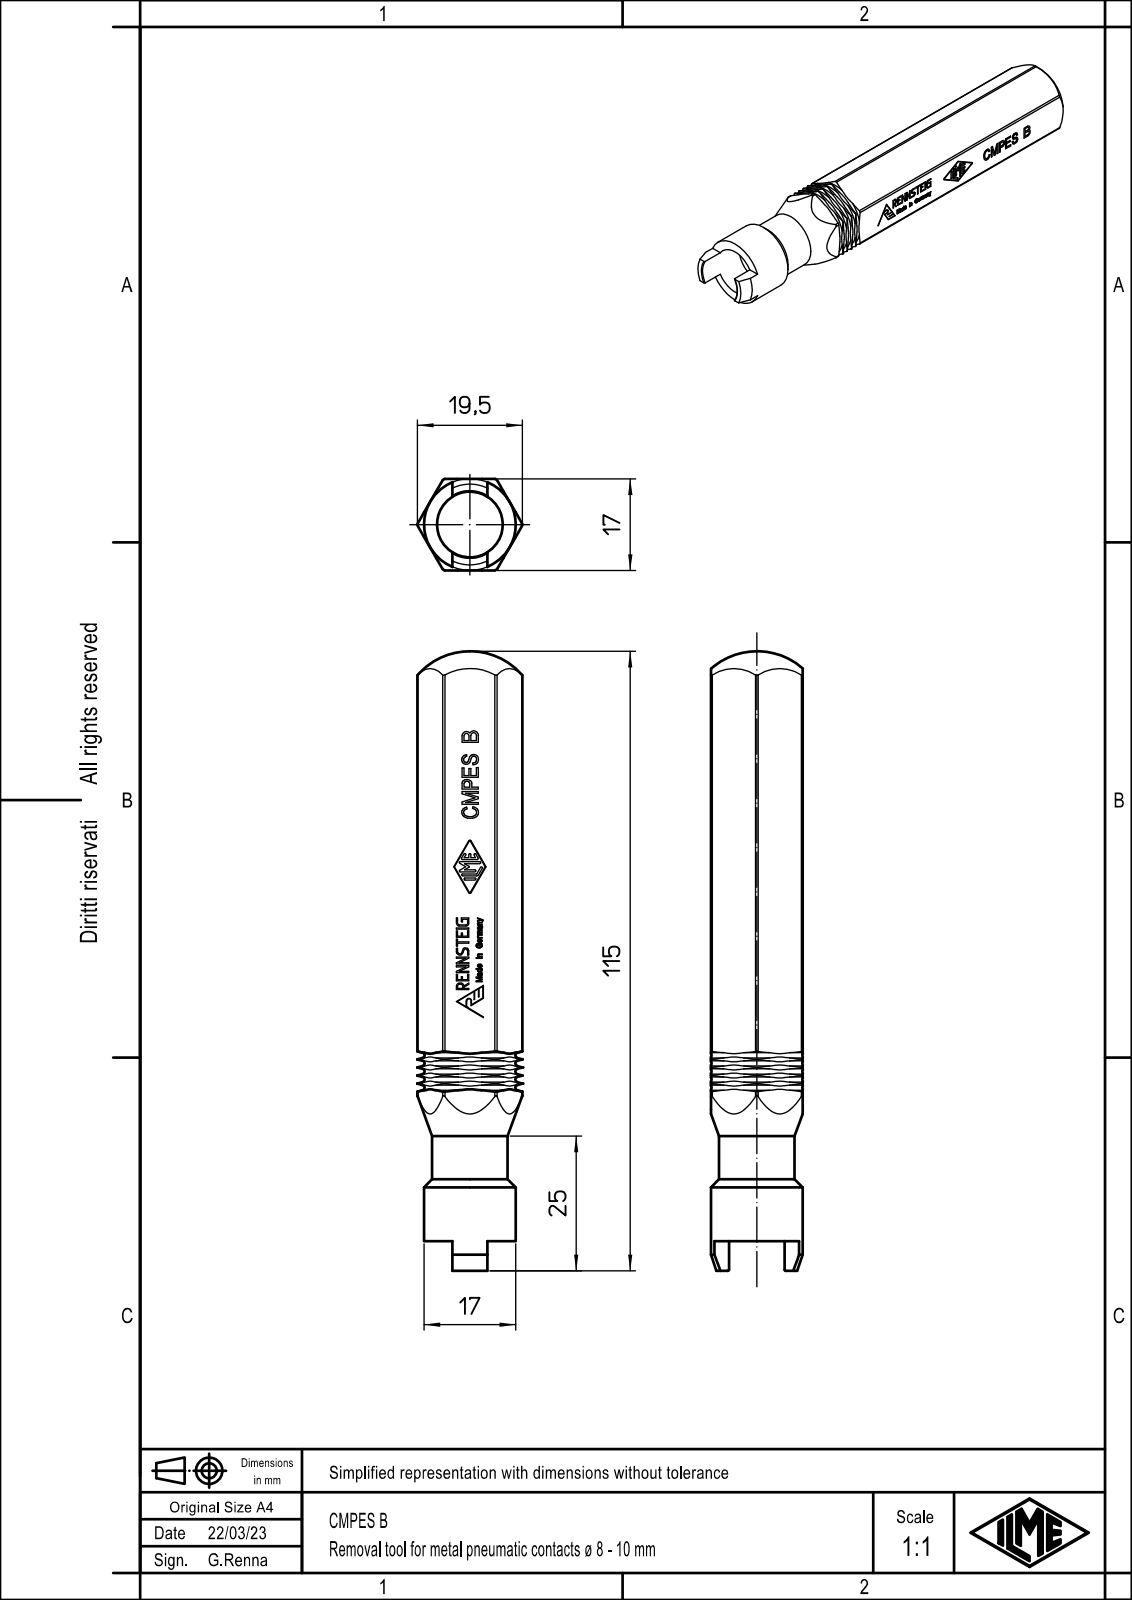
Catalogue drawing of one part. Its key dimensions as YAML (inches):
part_name: "CMPES B"
step_written_by: "Creo Elements/Direct Modeling 20.1B 02-Apr-2019 (C) Parametric Technology GmbH (AUTOMOTIVE_DESIGN)"
units: inches
bodies: {solids: 1, faces: 214, planar: 90, cylindrical: 42, other: 82}
overall_size: [4.528, 0.767, 0.669]
volume: 1.502
surface_area: 11.11
round_holes:
  - {diameter: 0.48, count: 1}
round_bosses_or_shafts:
  - {diameter: 0.669, count: 1}
  - {diameter: 0.551, count: 1}
partial_cylinders:
  - {radius: 0.02, count: 6}
face_to_face_distances: [0.669, 0.256, 0.217]
